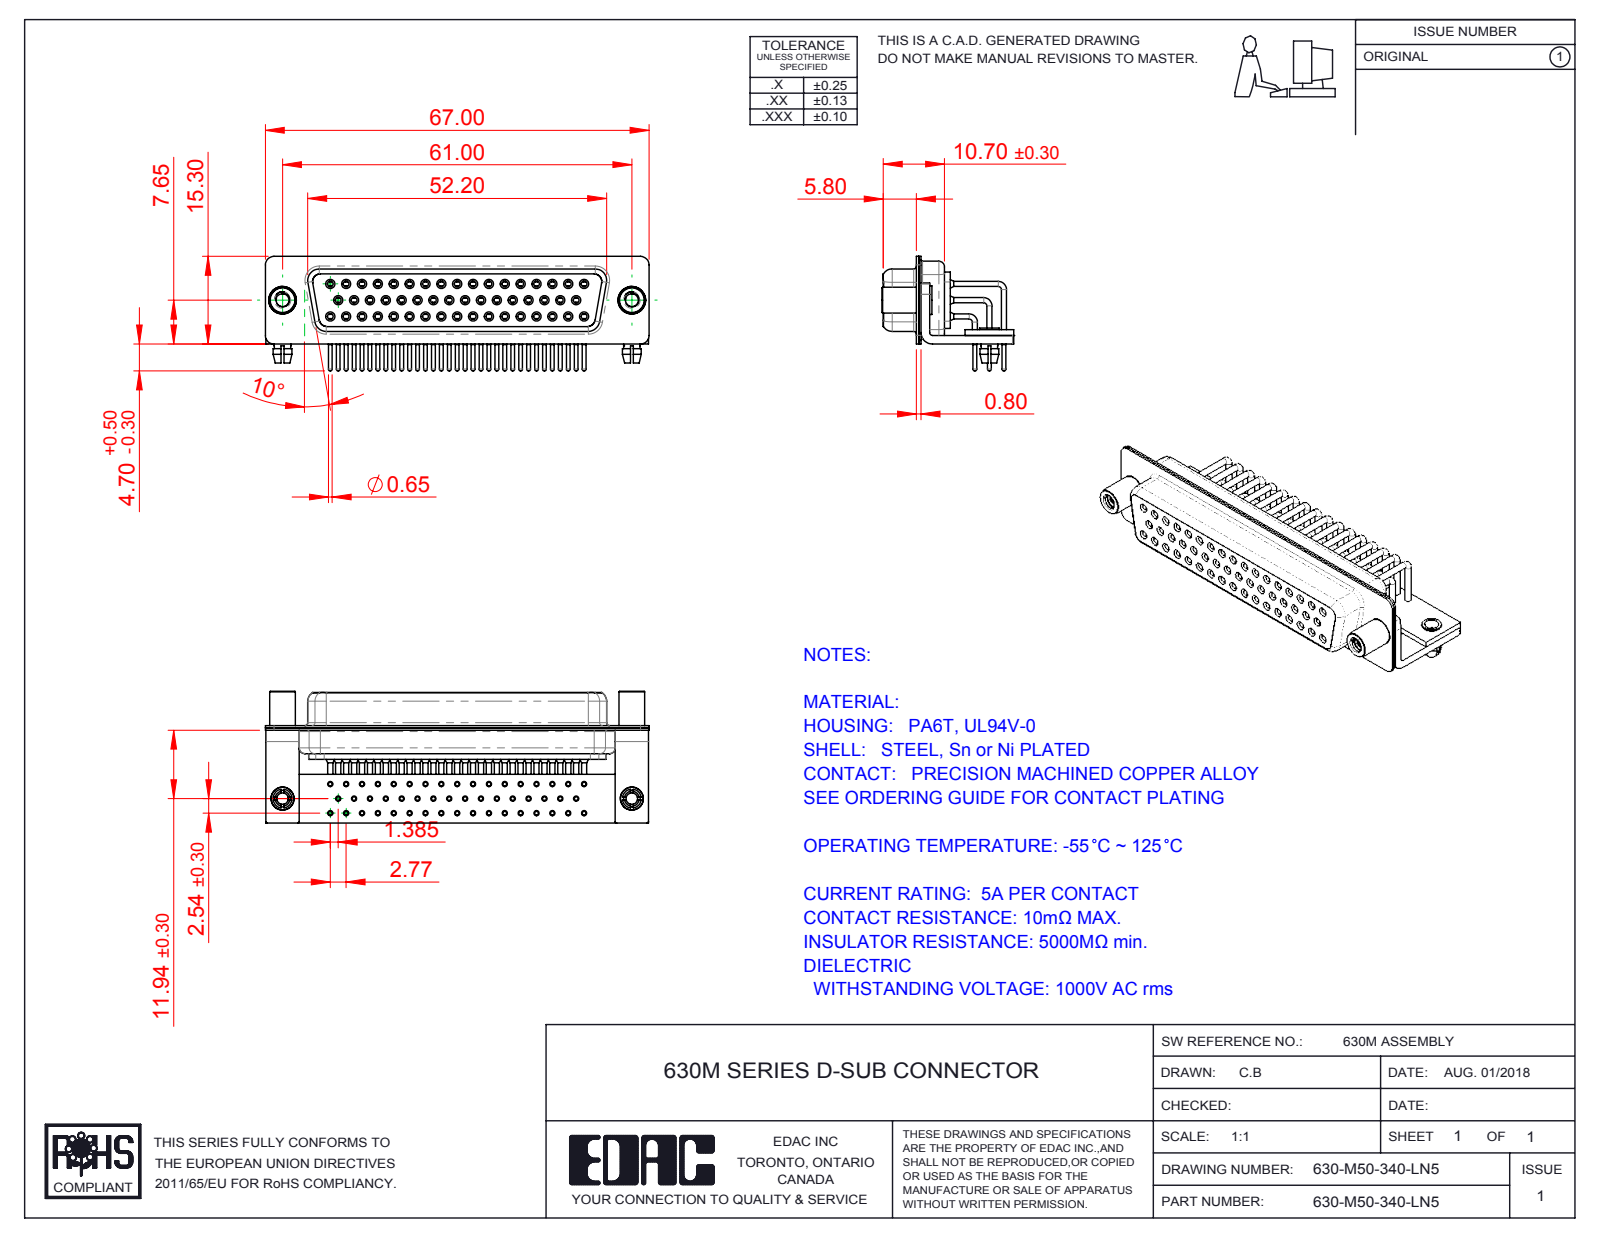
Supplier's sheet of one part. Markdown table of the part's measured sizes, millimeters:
| quantity | value |
| --- | --- |
| part name | 630M Contact Row 2_50 Contacts; 630M Shell Rear_50 Contacts; 630M Board Lock_50 Contacts; 630M Contact Row 1_50 Contacts (+7 more) |
| STEP written by | SolidWorks 2016 (CONFIG_CONTROL_DESIGN) |
| units | millimeters |
| bodies | 60 solids, 3221 faces (893 planar, 1483 cylindrical, 845 other) |
| overall size | 67 × 23 × 20 |
| volume | 8 037 mm³ |
| surface area | 19 165 mm² |
| round holes (diameter × count) | 2 × 52, 0.9 × 50, 1 × 50, 1.1 × 50, 1.7 × 50, 1.8 × 50, 2.26 × 2, 2.5 × 2, 3.2 × 2, 4 × 2, 4.8 × 2 |
| round bosses / shafts (diameter × count) | 0.9 × 59, 1.6 × 50, 1.5 × 50, 0.65 × 50, 5 × 2, 4.9 × 2, 4.5 × 2, 4 × 2 |
| partial cylindrical surfaces (radius × count) | 0.25 × 16, 1.5 × 16, 2 × 13, 1.35 × 8, 1.6 × 8, 0.5 × 5, 0.6 × 4, 0.65 × 4 |
| main face-to-face distances | 0.4, 1, 2.2, 0.85, 1.35, 11.85, 12.25, 5.8, 0.8, 5.9 |
| hole center spacings | 2.77, 5.54, 8.31, 11.08, 13.85, 16.62, 3.16, 19.39 |
